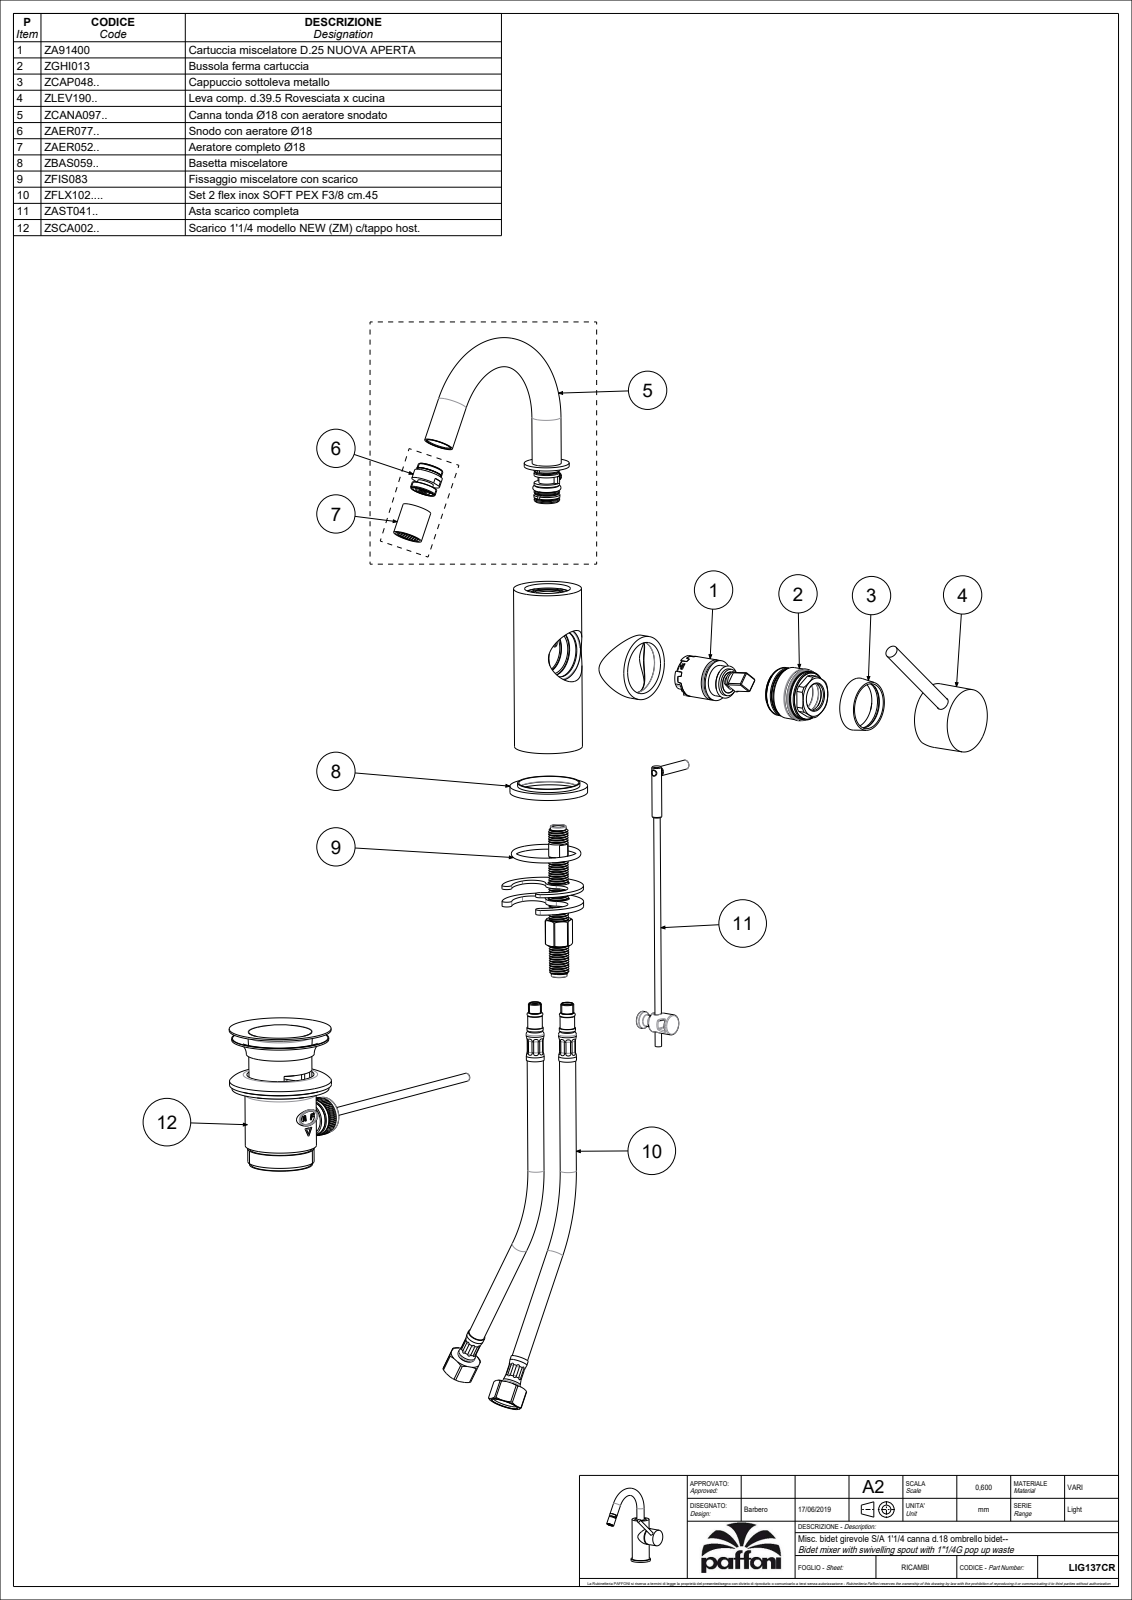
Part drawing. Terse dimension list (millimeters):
name: LIG137CR
written by: CREO PARAMETRIC BY PTC INC, 2020044 (CONFIG_CONTROL_DESIGN)
unit: mm
bodies: 0 solids, 125 faces (52 planar, 52 cylindrical, 21 other)
size: 190.5 × 161.04 × 79.15
holes: 1× ⌀3
bosses: 2× ⌀18, 1× ⌀48, 1× ⌀42, 1× ⌀39.5, 1× ⌀10, 1× ⌀7.9, 1× ⌀7.6, 1× ⌀6
rounds: 8× R1, 2× R0.8, 1× R3.5, 1× R5, 1× R6.4
face distances: 4, 104, 100, 10, 25.15, 15.15, 18.5, 21, 2.5, 24.15
